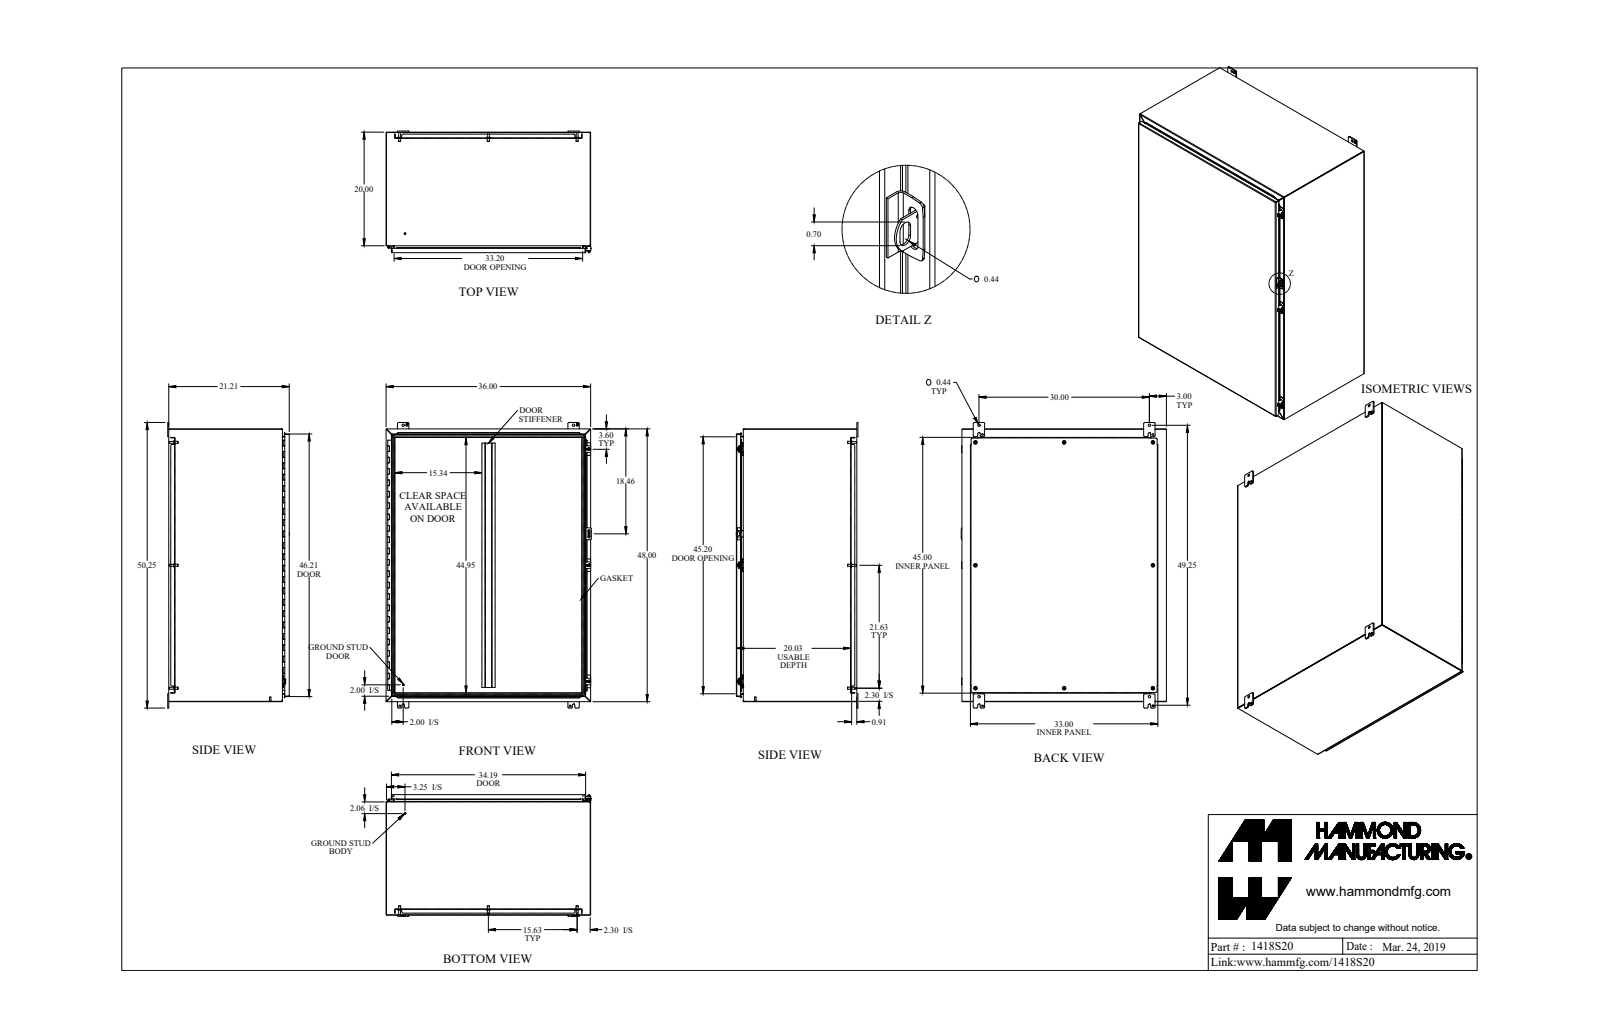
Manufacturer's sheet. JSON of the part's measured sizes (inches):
{"part_name": "1418S20_Default", "step_written_by": "SolidWorks 2019 (CONFIG_CONTROL_DESIGN)", "units": "inches", "bodies": {"solids": 39, "faces": 1475, "planar": 883, "cylindrical": 522, "other": 70}, "overall_size": [50.25, 36.094, 21.437], "volume_in3": 732.8, "surface_area_in2": 19253, "round_holes": [[0.5, 8], [0.313, 4], [0.437, 4], [0.213, 3], [0.125, 1], [0.187, 1]], "round_bosses_or_shafts": [[0.65, 8], [0.375, 8], [0.33, 8], [0.39, 3], [0.313, 2], [0.25, 2], [0.287, 1]], "partial_cylinders_radius": [[0.188, 38], [0.048, 31], [0.25, 20], [0.143, 19], [0.116, 16], [0.12, 12], [0.036, 10], [0.108, 10]], "face_to_face_distances": [0.072, 21.113, 35.928, 21.041, 21.185, 0.095, 20.176, 20.104, 0.937, 1.009], "hole_center_spacings": [1.735, 30, 38.003, 45.986, 47.75, 56.392, 26.679, 31.25]}
